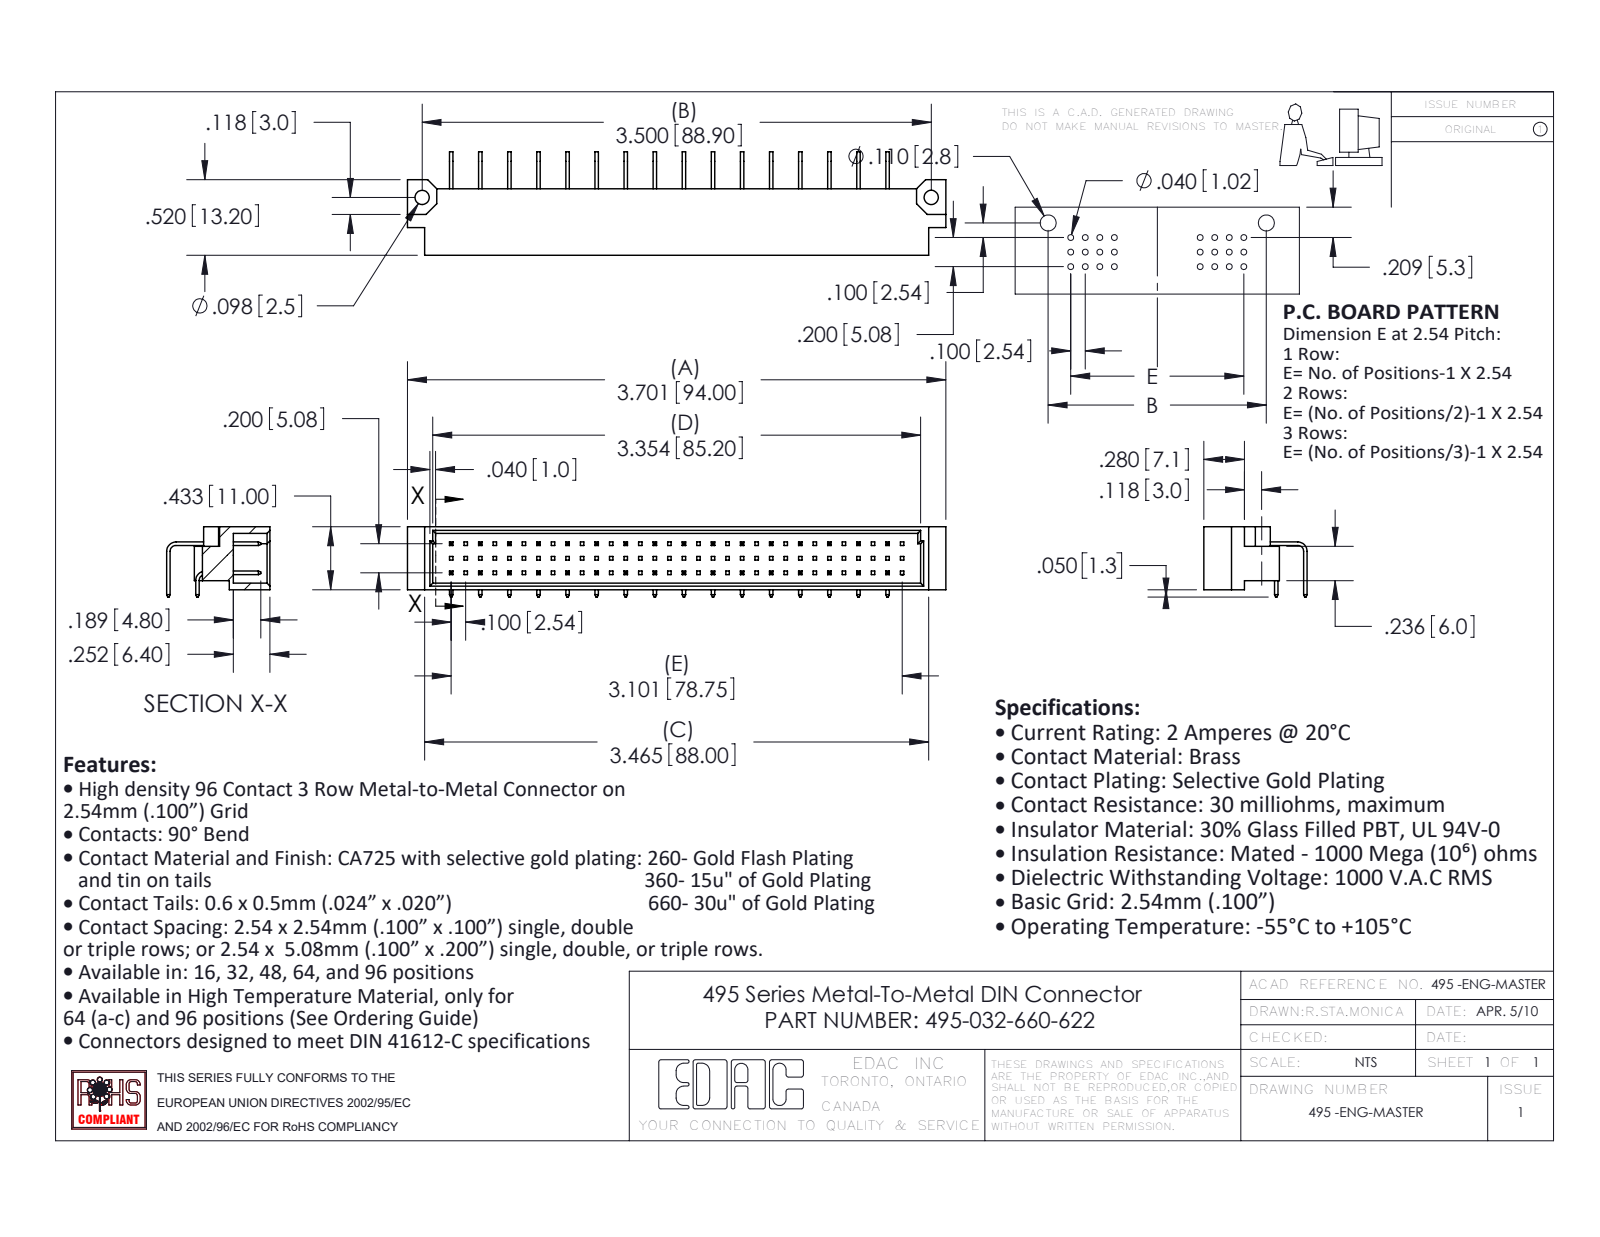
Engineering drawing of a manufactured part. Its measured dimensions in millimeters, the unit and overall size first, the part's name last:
Units: millimetres
Overall size (bounding box): 94 × 18.05 × 12.27
Round holes (diameter × count): ⌀2.49 ×2
Partial cylindrical surfaces — rounded edges, fillets, slot ends (radius × count): R1.02 ×2, R1.65 ×2
Main face-to-face distances: 1.14, 9.86, 5.08, 5.2, 11, 0.61, 8.72, 1.6, 9.4, 0.46
Hole centre spacings: 88.9
Volume: 6 161 mm³ · Surface area: 8 378 mm²
Bodies: 33 solids, 1009 faces (941 planar, 68 cylindrical, 0 other)
Part name (STEP PRODUCT): 495-290-1; 495-290-3; 495 Part_96; 495-032-660-622
STEP written by: SolidWorks 2020 (AUTOMOTIVE_DESIGN)
